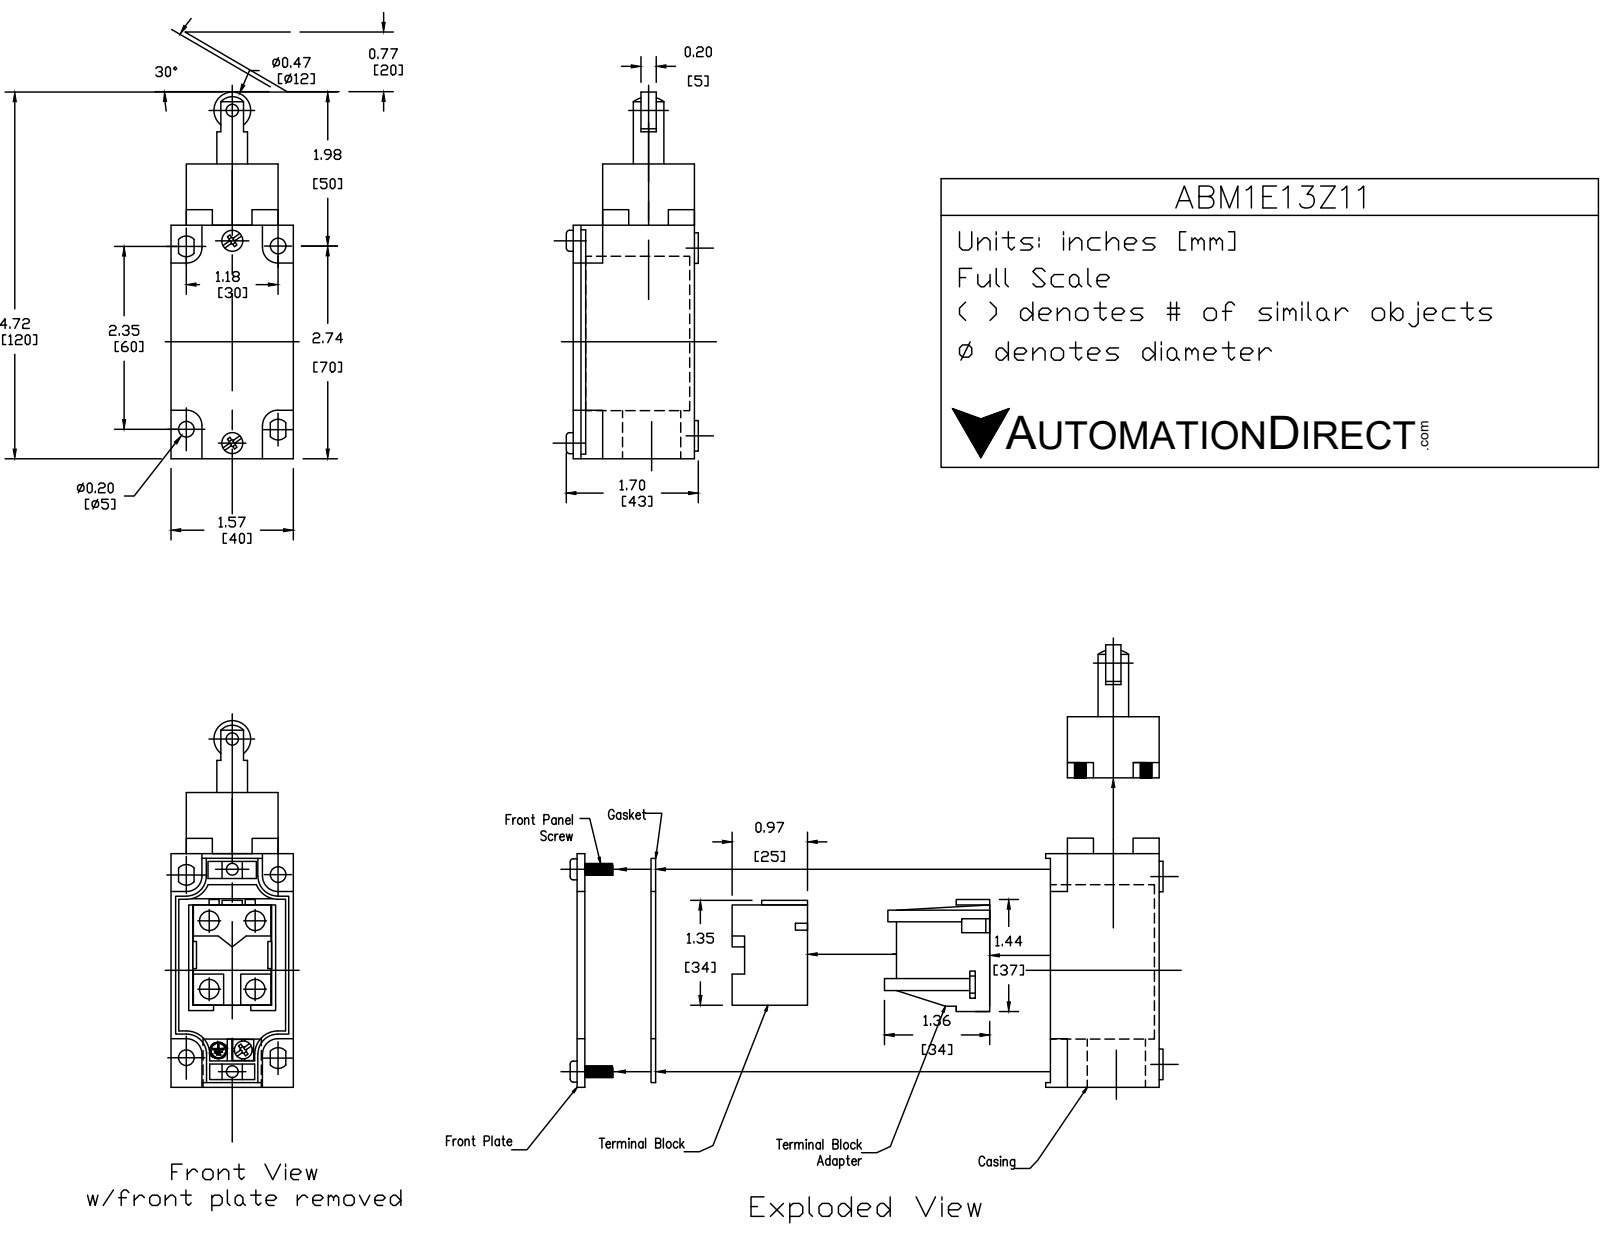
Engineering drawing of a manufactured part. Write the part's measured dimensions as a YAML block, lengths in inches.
part_name: "ABM1E13Z11"
step_written_by: "SolidWorks 2017 (AUTOMOTIVE_DESIGN)"
units: inches
bodies: {solids: 4, faces: 167, planar: 77, cylindrical: 68, other: 22}
overall_size: [4.72, 1.705, 1.575]
volume: 7.844
surface_area: 38.88
round_holes:
  - {diameter: 0.205, count: 2}
  - {diameter: 0.394, count: 1}
  - {diameter: 0.669, count: 1}
  - {diameter: 0.748, count: 1}
round_bosses_or_shafts:
  - {diameter: 0.394, count: 4}
  - {diameter: 0.276, count: 2}
  - {diameter: 0.472, count: 1}
partial_cylinders:
  - {radius: 0.059, count: 16}
  - {radius: 0.039, count: 4}
  - {radius: 0.197, count: 4}
  - {radius: 0.128, count: 2}
  - {radius: 0.453, count: 1}
  - {radius: 0.472, count: 1}
face_to_face_distances: [1.575, 1.555, 1.181, 0.197, 1.378, 0.374, 3.012, 3.209, 0.591, 3.031]
hole_center_spacings: [0.039, 2.641]
